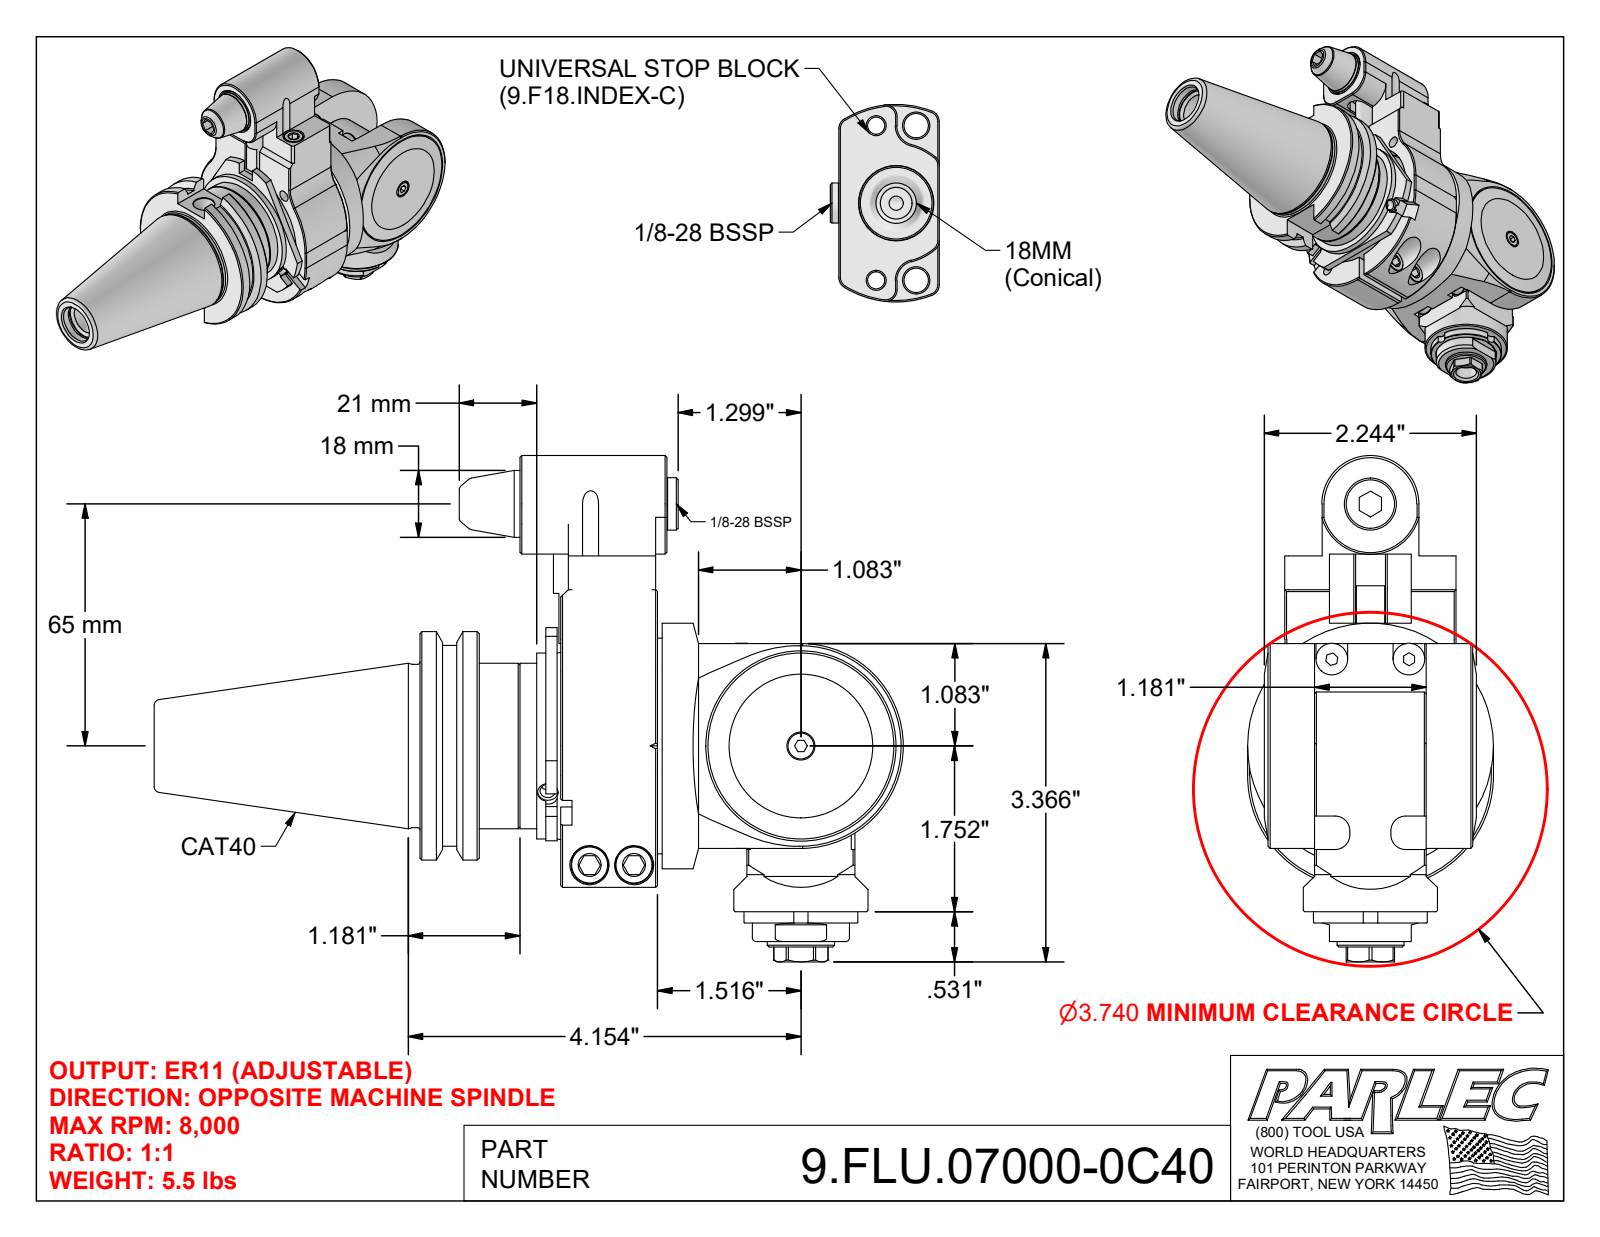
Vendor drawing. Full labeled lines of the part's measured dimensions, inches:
Part name (STEP PRODUCT): 9.FLU.07000-0C40; FLU0700-0000005C_446
STEP written by: Autodesk Inventor 2022 (AUTOMOTIVE_DESIGN)
Units: inches
Bodies: 2 solids, 611 faces (327 planar, 158 cylindrical, 126 other)
Overall size (bounding box): 7.923 × 5.354 × 2.598
Volume: 23.69 in³ · Surface area: 137.1 in²
Round holes (diameter × count): ⌀0.295 ×4, ⌀0.197 ×3, ⌀0.165 ×2, ⌀0.217 ×2, ⌀0.256 ×2, ⌀0.37 ×2, ⌀0.413 ×2, ⌀0.098 ×1, ⌀0.118 ×1, ⌀0.236 ×1, ⌀0.354 ×1, ⌀0.362 ×1
Round bosses / shafts (diameter × count): ⌀0.335 ×6, ⌀0.394 ×3, ⌀0.276 ×3, ⌀0.709 ×2, ⌀0.236 ×2, ⌀2.598 ×1, ⌀2.5 ×1, ⌀2.283 ×1
Partial cylindrical surfaces — rounded edges, fillets, slot ends (radius × count): R0.118 ×6, R0.157 ×6, R0.039 ×4, R0.083 ×4, R0.197 ×4, R0.512 ×3, R0.315 ×2, R1.181 ×2
Main face-to-face distances: 1.024, 0.531, 0.945, 0.079, 0.039, 0.217, 0.177, 1.181, 1.713, 0.118
Hole centre spacings: 0.276, 0.014, 0.472, 0.551, 1.217, 1.256, 1.457, 1.643
